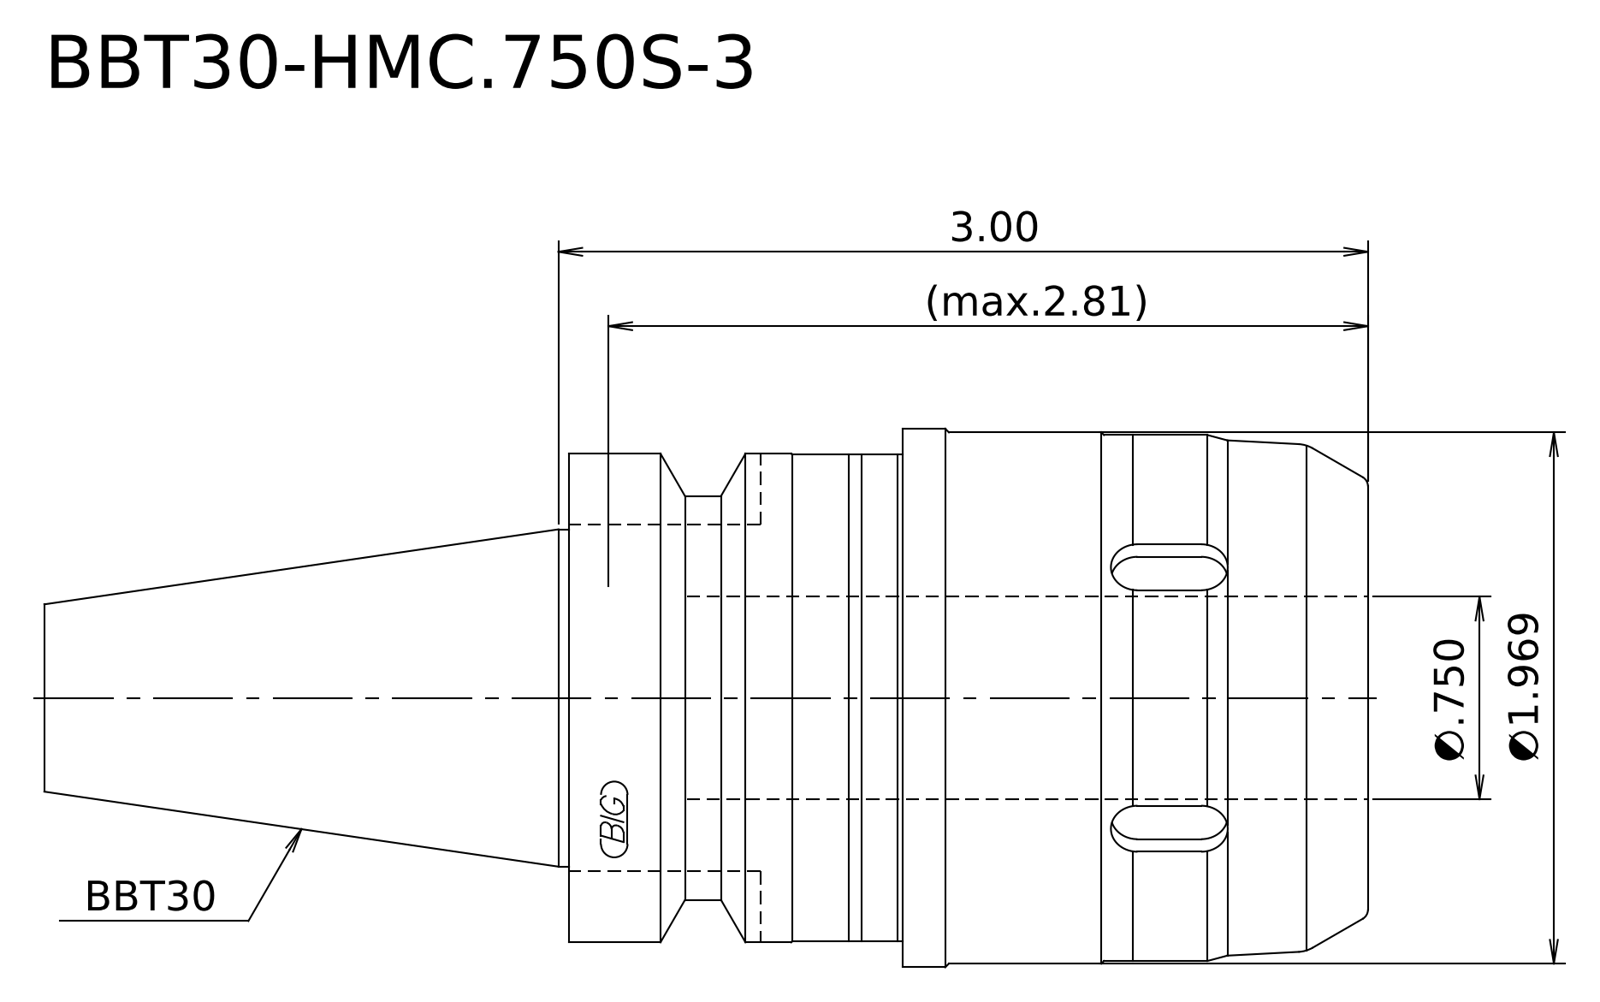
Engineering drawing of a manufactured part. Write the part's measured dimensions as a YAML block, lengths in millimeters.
step_written_by: "Kubotek KeyCreator 2011 V10.0.2 (22737) (automotive_design)"
units: millimeters
bodies: {solids: 1, faces: 21, planar: 4, cylindrical: 8, other: 9}
overall_size: [124.6, 50.7, 50.7]
volume: 155797
surface_area: 18601
round_bosses_or_shafts:
  - {diameter: 50.7, count: 1}
  - {diameter: 50, count: 1}
  - {diameter: 49.5, count: 1}
  - {diameter: 46, count: 1}
  - {diameter: 45.8, count: 1}
  - {diameter: 38, count: 1}
  - {diameter: 31.75, count: 1}
face_to_face_distances: [75.2, 43.8, 31.4, 124.6, 80.8, 49.4]
